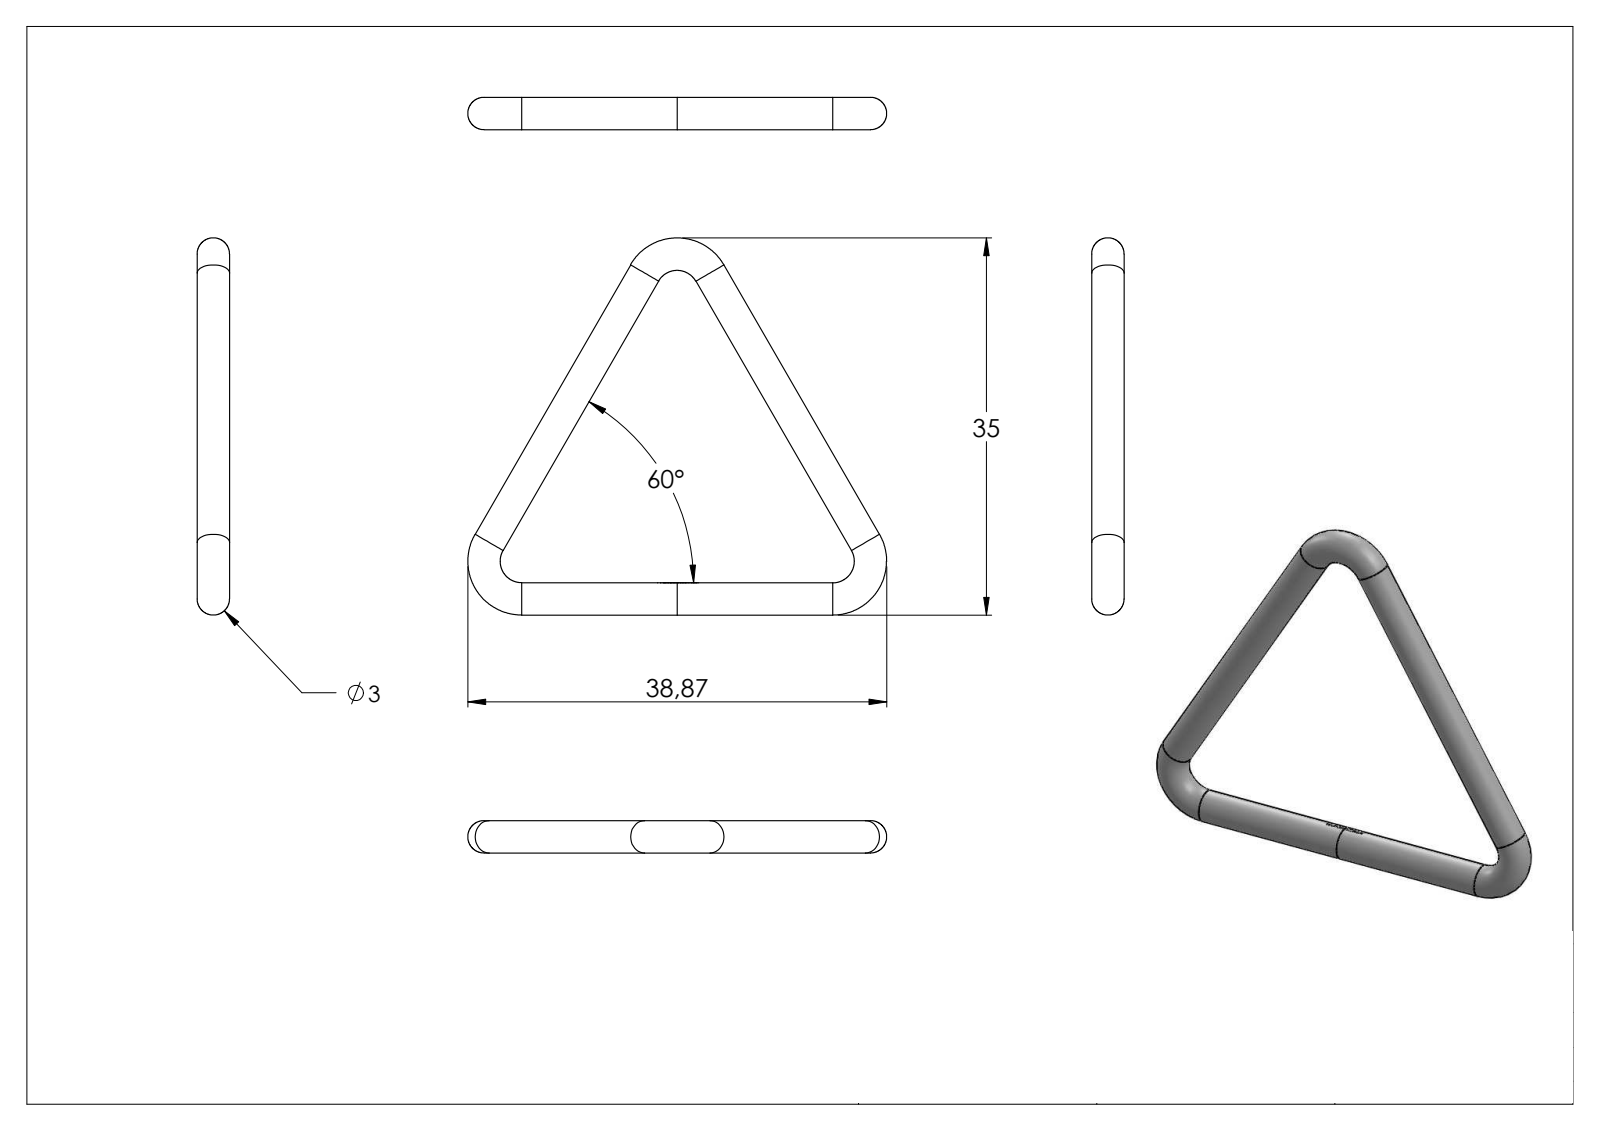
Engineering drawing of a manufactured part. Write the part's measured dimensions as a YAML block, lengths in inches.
part_name: "100077335"
step_written_by: "SolidWorks 2015 (CONFIG_CONTROL_DESIGN)"
units: inches
bodies: {solids: 1, faces: 225, planar: 84, cylindrical: 27, other: 114}
overall_size: [1.53, 1.378, 0.118]
volume: 0.047
surface_area: 1.589
round_bosses_or_shafts:
  - {diameter: 0.118, count: 3}
partial_cylinders:
  - {radius: 0.055, count: 1}
face_to_face_distances: [0.023, 0.016, 0.024, 0.013, 0.061, 0.076, 0.026, 0.029, 0.036, 0.025]
